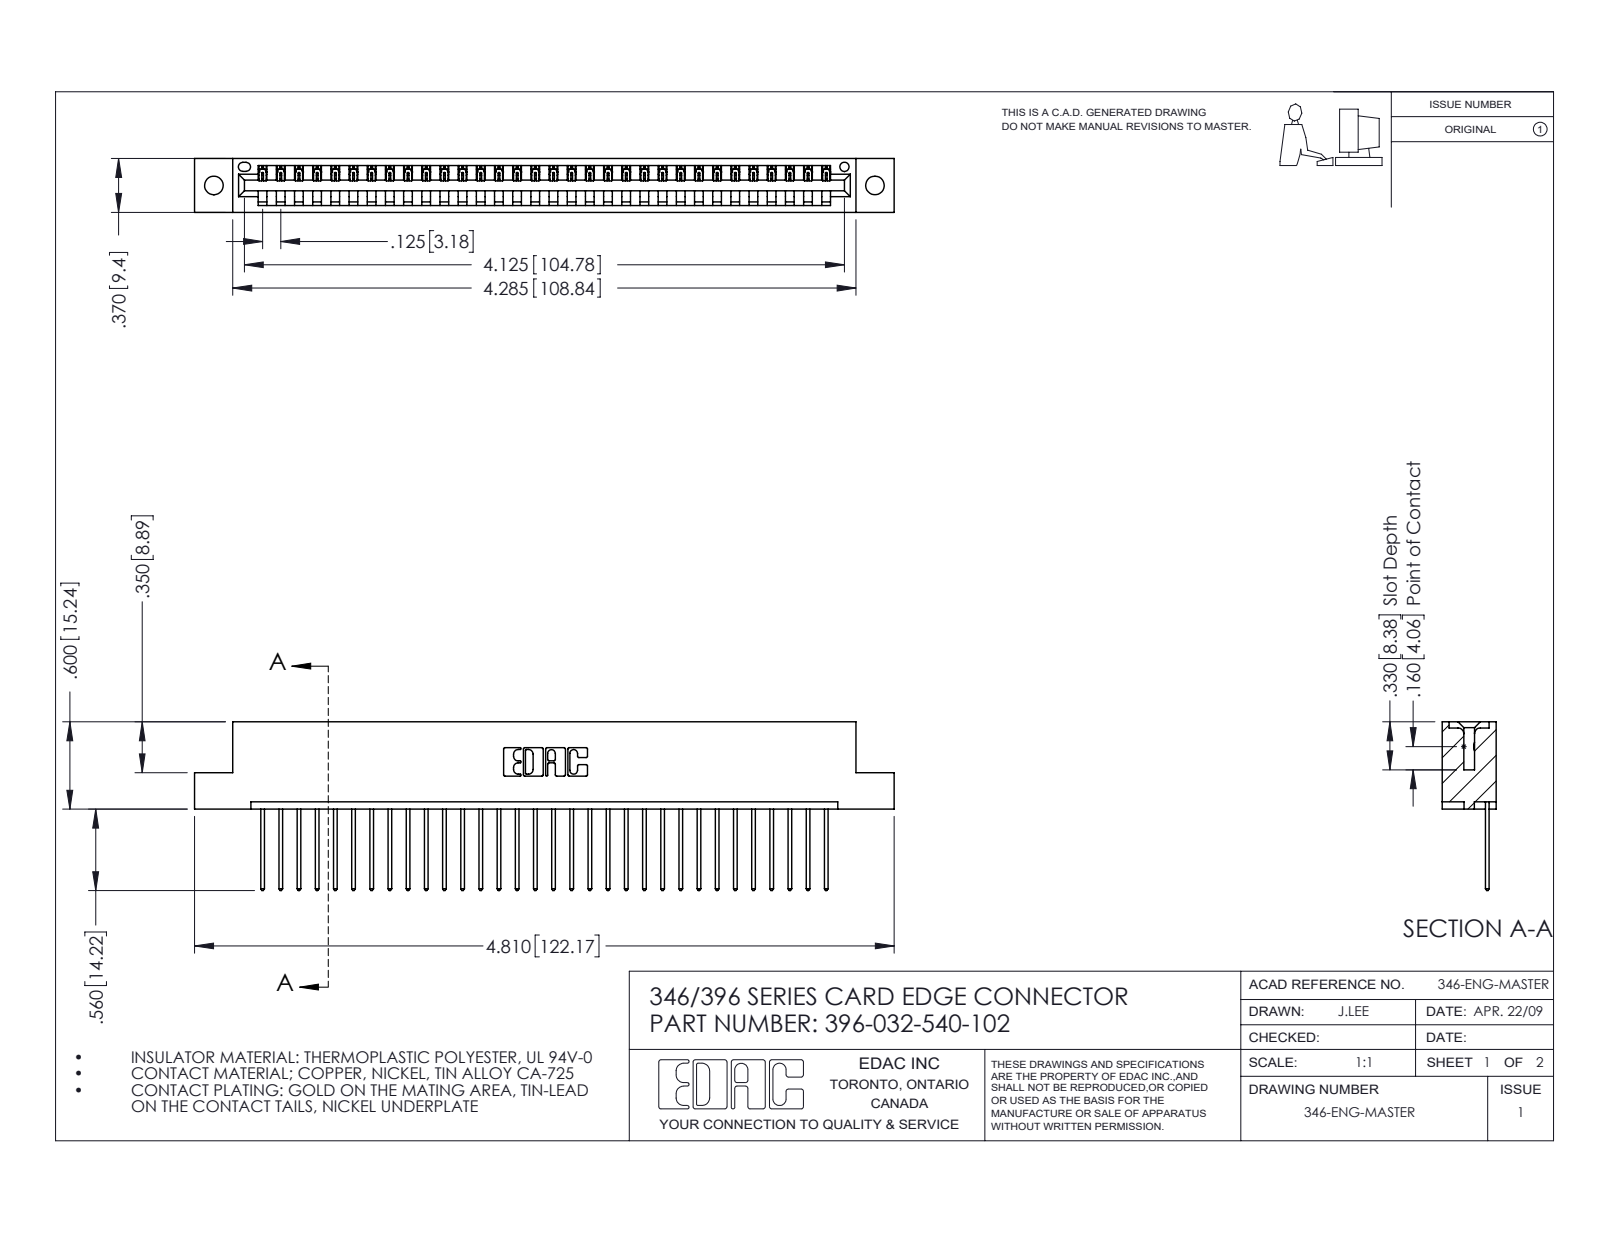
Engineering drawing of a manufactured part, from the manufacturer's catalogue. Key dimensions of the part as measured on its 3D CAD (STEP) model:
Part name (STEP PRODUCT): 396-032-540-102; 346 Part_Flush Mounting Lugs - 0.128 Dia; 345-292-001_345-293-140
STEP written by: SolidWorks 2016 (CONFIG_CONTROL_DESIGN)
Units: inches
Bodies: 33 solids, 1978 faces (1356 planar, 622 cylindrical, 0 other)
Overall size (bounding box): 4.81 × 1.16 × 0.37
Volume: 0.71 in³ · Surface area: 22.44 in²
Round holes (diameter × count): ⌀0.128 ×2, ⌀0.064 ×1
Partial cylindrical surfaces — rounded edges, fillets, slot ends (radius × count): R0.006 ×64, R0.01 ×64, R0.01 ×22, R0.007 ×6, R0.031 ×6, R0.026 ×3, R0.031 ×2, R0.04 ×2
Main face-to-face distances: 0.048, 0.322, 0.37, 0.25, 0.072, 0.298, 0.025, 0.148, 0.222, 0.1
Hole centre spacings: 0.246, 4.337, 4.545
